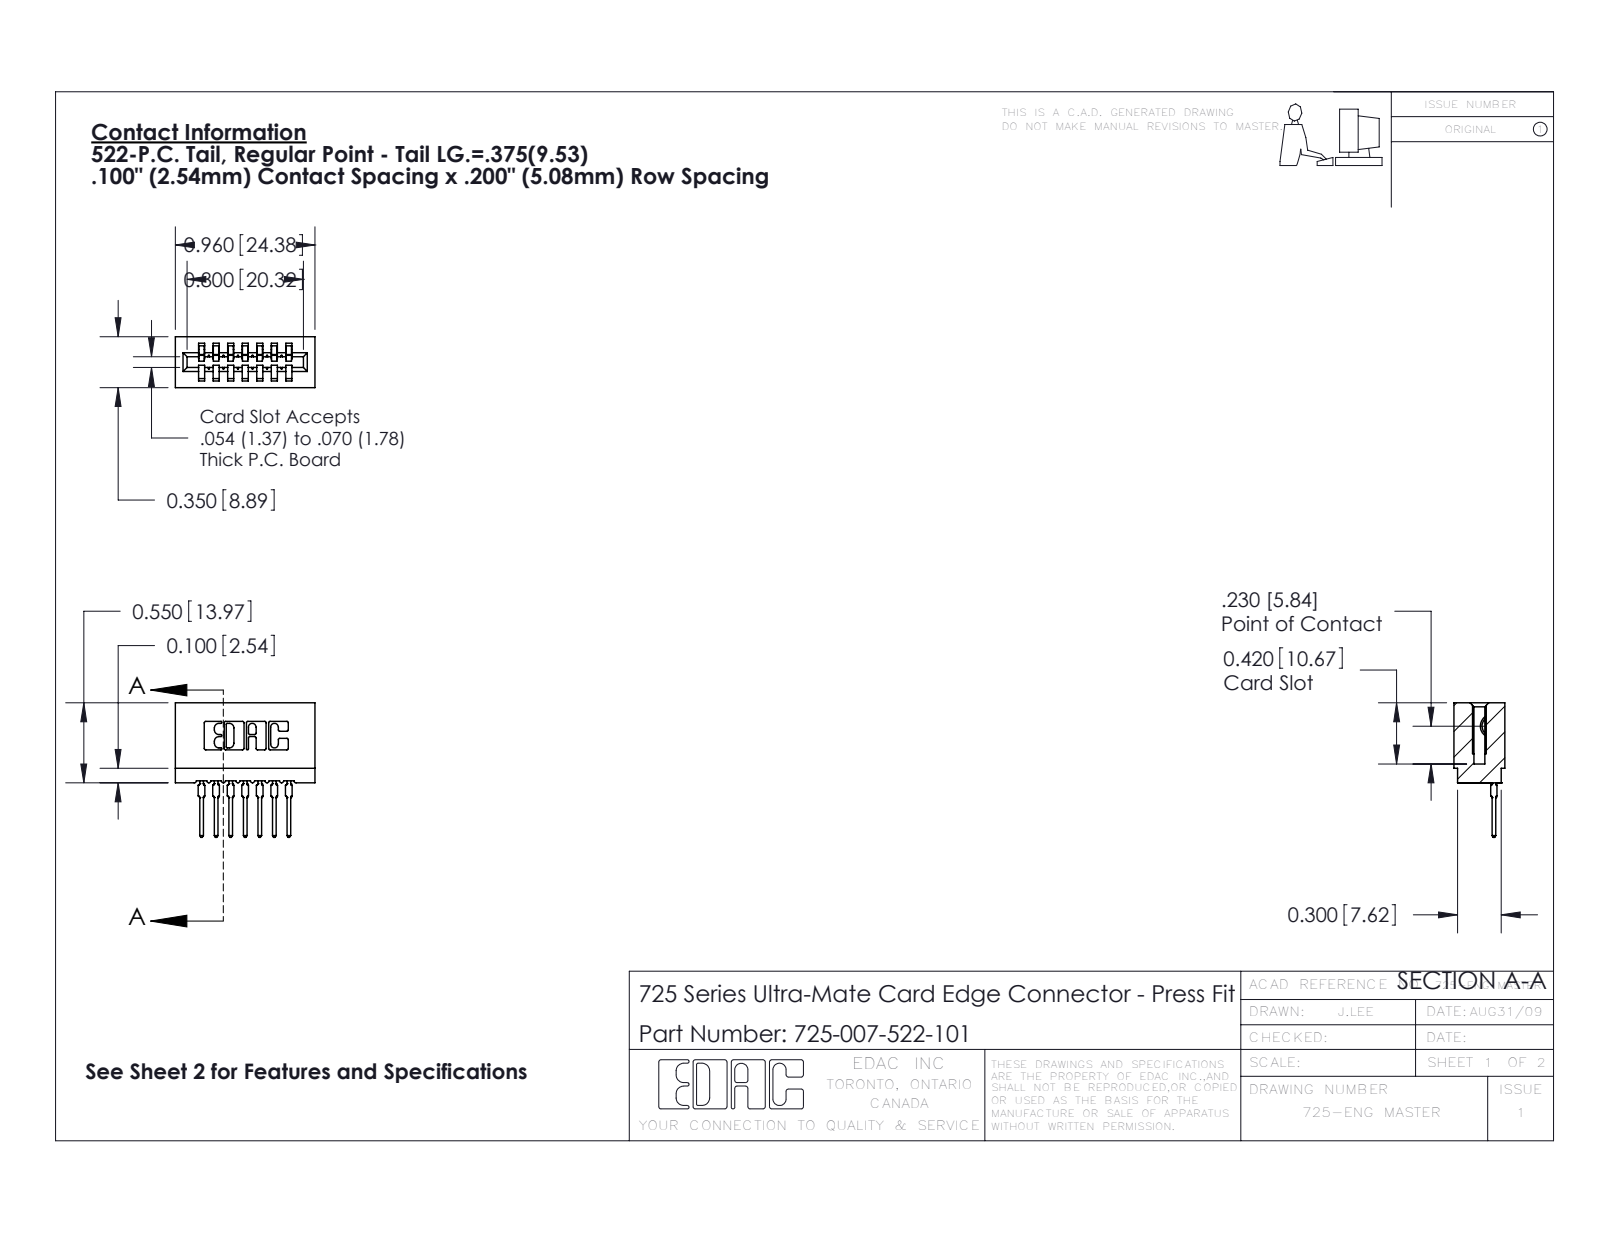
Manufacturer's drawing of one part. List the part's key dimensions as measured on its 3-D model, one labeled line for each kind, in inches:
Part name (STEP PRODUCT): 725-007-522-101; 725 Part_Insulator Option - 01; 745-292-001_522
STEP written by: SolidWorks 2016 (CONFIG_CONTROL_DESIGN)
Units: inches
Bodies: 8 solids, 879 faces (524 planar, 173 cylindrical, 182 other)
Overall size (bounding box): 0.96 × 0.925 × 0.35
Volume: 0.125 in³ · Surface area: 5.158 in²
Partial cylindrical surfaces — rounded edges, fillets, slot ends (radius × count): R0.01 ×22, R0.015 ×14, R0.021 ×14, R0.007 ×6, R0.031 ×6, R0.005 ×4, R0.011 ×4, R0.026 ×3
Main face-to-face distances: 0.1, 0.2, 0.3, 0.042, 0.4, 0.142, 0.058, 0.242, 0.158, 0.5
